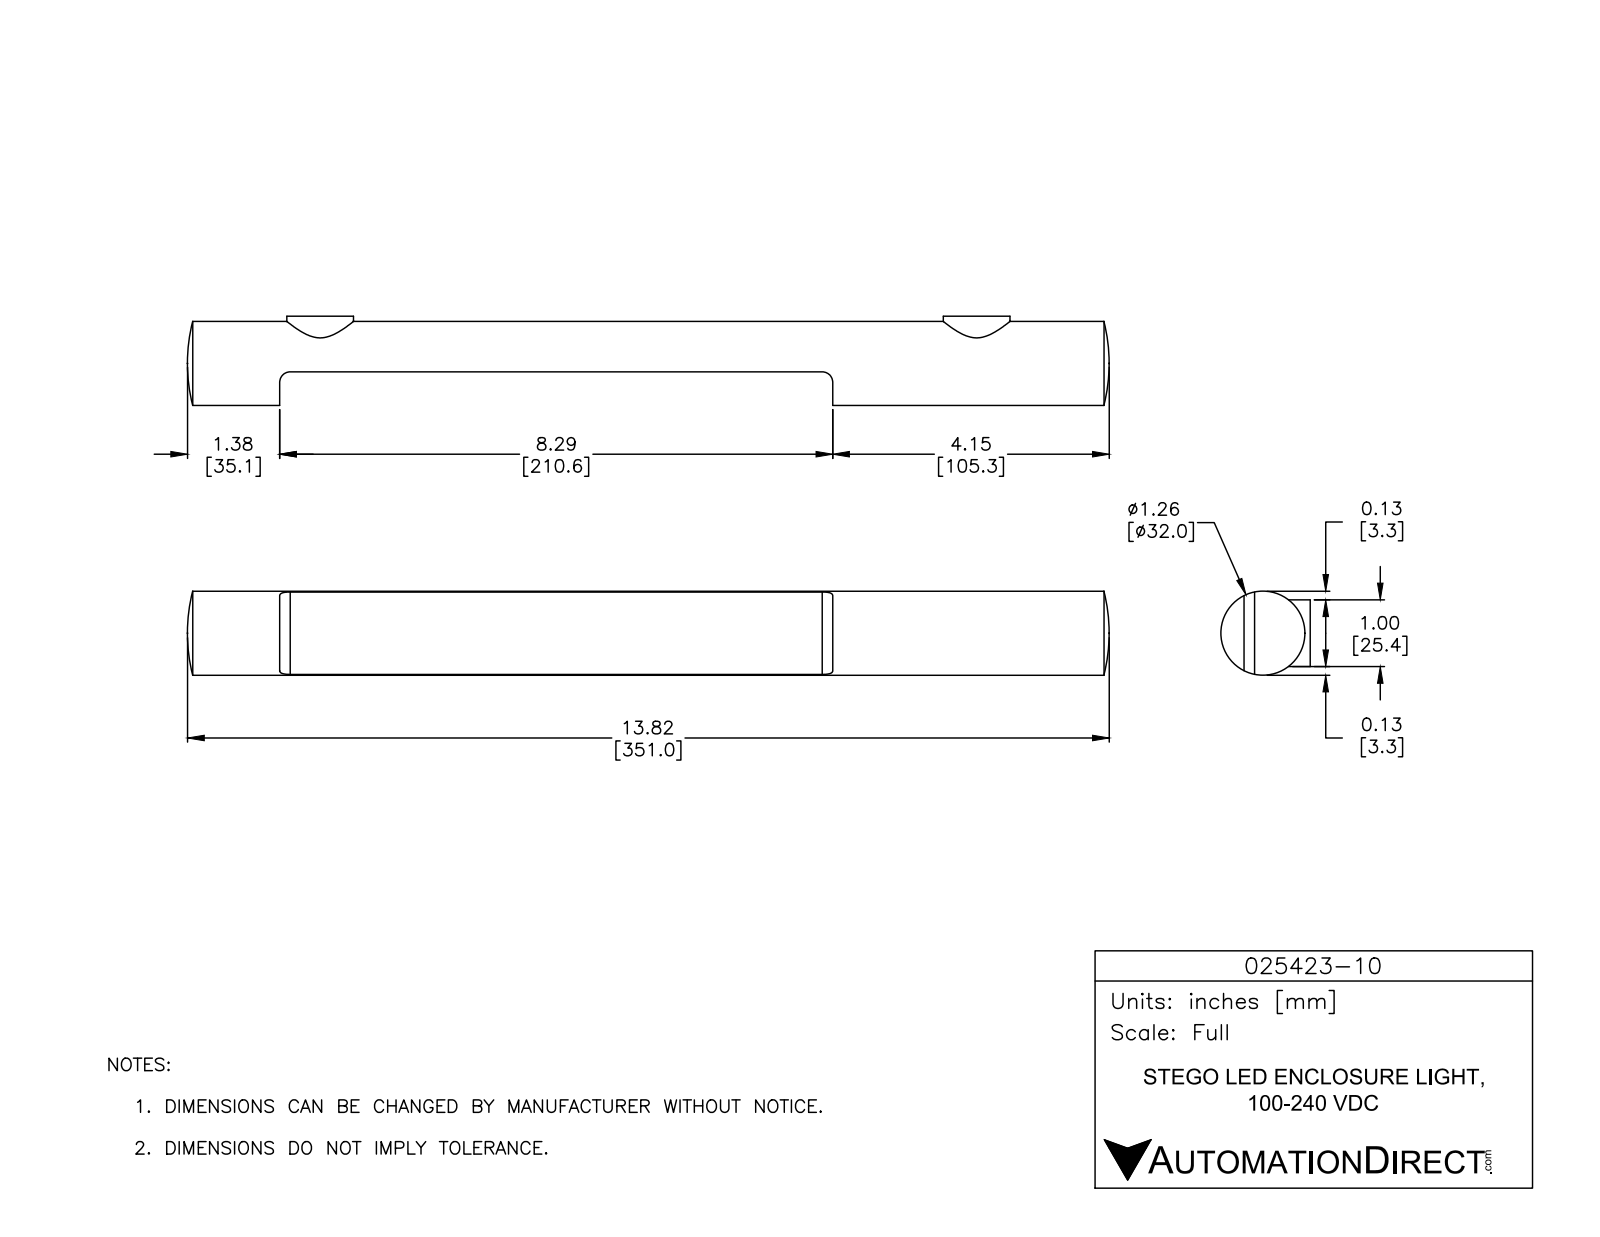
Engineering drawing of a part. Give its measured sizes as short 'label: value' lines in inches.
name: PRODUCT_NAME_1
written by: ACIS (CONFIG_CONTROL_DESIGN)
unit: in
bodies: 1 solid, 17 faces (5 planar, 8 cylindrical, 4 other)
size: 13.819 × 1.339 × 1.26
volume: 13.49 in³; area: 54.37 in²
bosses: 2× ⌀1, 1× ⌀1.26
rounds: 2× R0.157
face distances: 0.835, 8.291
